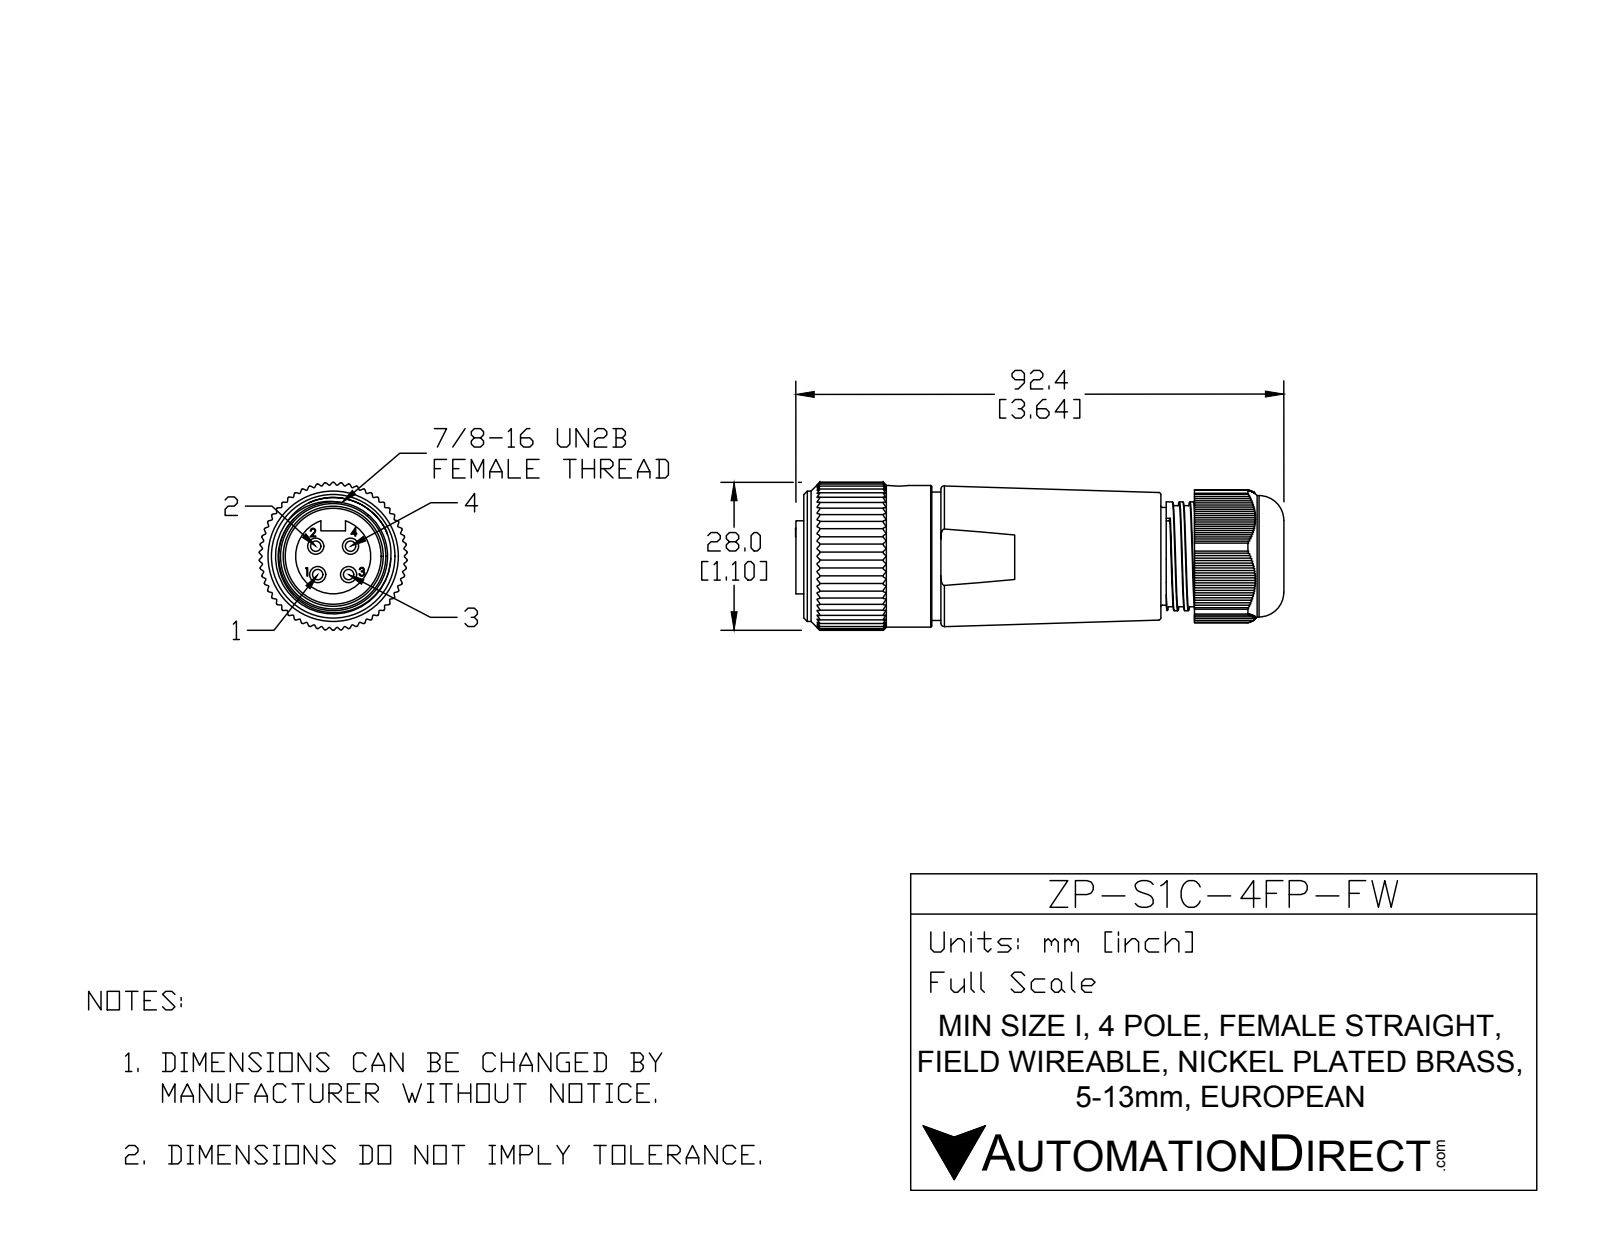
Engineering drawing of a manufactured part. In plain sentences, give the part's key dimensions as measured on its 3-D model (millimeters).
The part is named "ZP-S1C-4FP-FW". Its 3-D file was written by "SolidWorks 2015 (AUTOMOTIVE_DESIGN)". It is 4 solids with 796 faces: 448 planar, 302 cylindrical and 46 other. Overall it measures 92.42 by 27.99 by 27.98 millimeters. Its volume is 41 651 cubic millimeters and its surface area 14 420 square millimeters. Round holes: 4 of diameter 3.05, 1 of diameter 3.56, 1 of diameter 13.46, 1 of diameter 20.58, 1 of diameter 21.57, 1 of diameter 24.2, 1 of diameter 25.4. Round bosses or shafts: 1 of diameter 26.8, 1 of diameter 24.68, 1 of diameter 24.3, 1 of diameter 22.99, 1 of diameter 20.6, 1 of diameter 18.14, 1 of diameter 14.22. Partial cylindrical surfaces (rounded edges, fillets, slot ends): 165 of radius 0.25, 1 of radius 13.23, 1 of radius 14. The main face-to-face distances are 68.63, 1.06, 0.35, 0.71, 6.35, 69.13, 8.79, 59.84, 1.41, 2.12. The hole center spacings are 3.81, 4.54, 5.39, 8.22, 5.84, 6.6.
